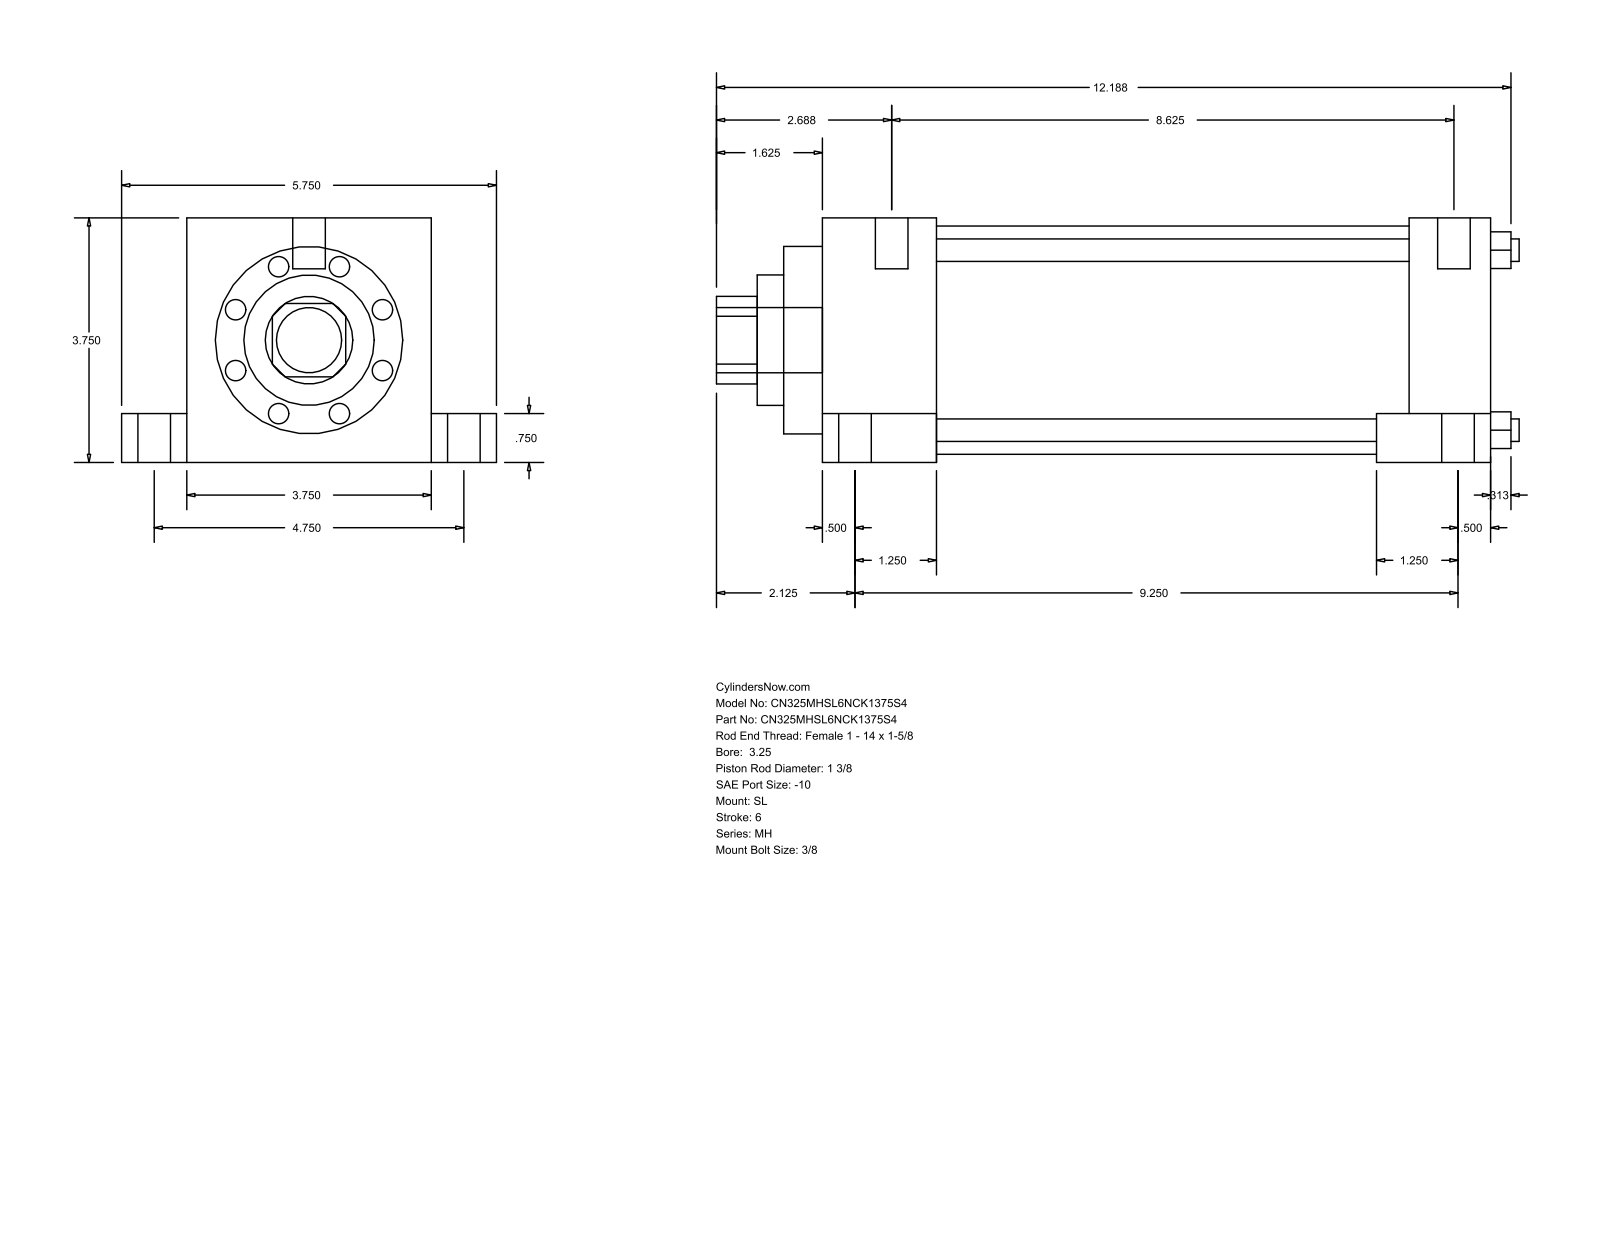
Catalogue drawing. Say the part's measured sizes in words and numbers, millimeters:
The part is named "MH_SL__0325_1.375". Its 3-D file was written by "GSSL Pune (CONFIG_CONTROL_DESIGN)". It is 0 solids with 110 faces: 77 planar, 33 cylindrical and 0 other. Overall it measures 312.74 by 146.05 by 95.25 millimeters. Round holes: 4 of diameter 8.76, 1 of diameter 34.92, 1 of diameter 50.8, 1 of diameter 73.03, 1 of diameter 88.9. Round bosses or shafts: 6 of diameter 12.7, 4 of diameter 19.05, 4 of diameter 5.56, 1 of diameter 25.4. Partial cylindrical surfaces (rounded edges, fillets, slot ends): 1 of radius 17.06. The main face-to-face distances are 95.24, 260.35, 44.45, 215.9, 25.41, 120.65, 19.05, 76.19, 228.61, 184.16. The hole center spacings are 49.57, 70.1, 99.14.
